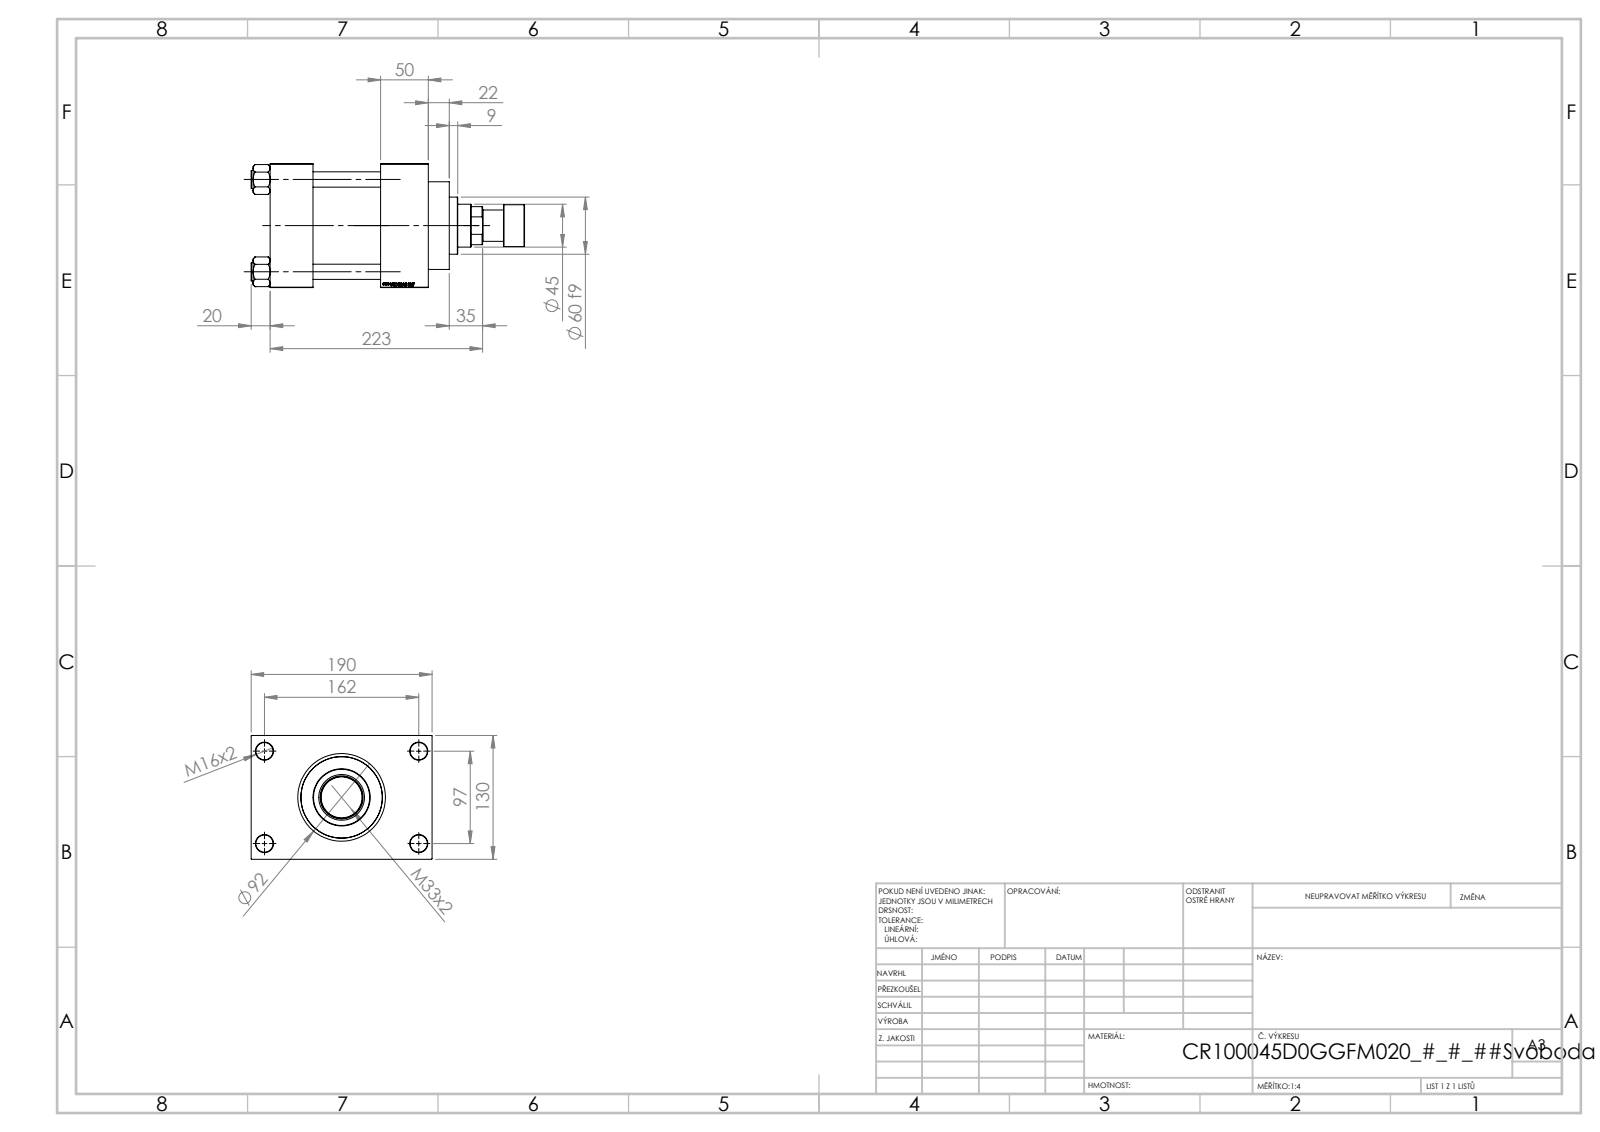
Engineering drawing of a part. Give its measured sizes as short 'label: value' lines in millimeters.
name: V215CR_VCP_D; NUT_M5_D; V215CR_D_TYCINKA; V215_VC_A (+2 more)
written by: SolidWorks 2019 (CONFIG_CONTROL_DESIGN)
unit: mm
bodies: 12 solids, 1165 faces (548 planar, 93 cylindrical, 524 other)
size: 287 × 190 × 130
volume: 2 659 000 mm³; area: 360 772 mm²
holes: 4× ⌀16, 4× ⌀18, 2× ⌀7, 2× ⌀26.44, 2× ⌀35, 1× ⌀31.5, 1× ⌀45, 1× ⌀48, 1× ⌀76, 1× ⌀85.5, 1× ⌀100
bosses: 4× ⌀19, 1× ⌀106, 1× ⌀92, 1× ⌀60, 1× ⌀44, 1× ⌀33
face distances: 130, 116, 45, 71, 166, 121, 50, 30, 160, 70
hole spacings: 32.55, 68.52, 94.41, 96.9, 102.27, 129.45, 161.73, 97
